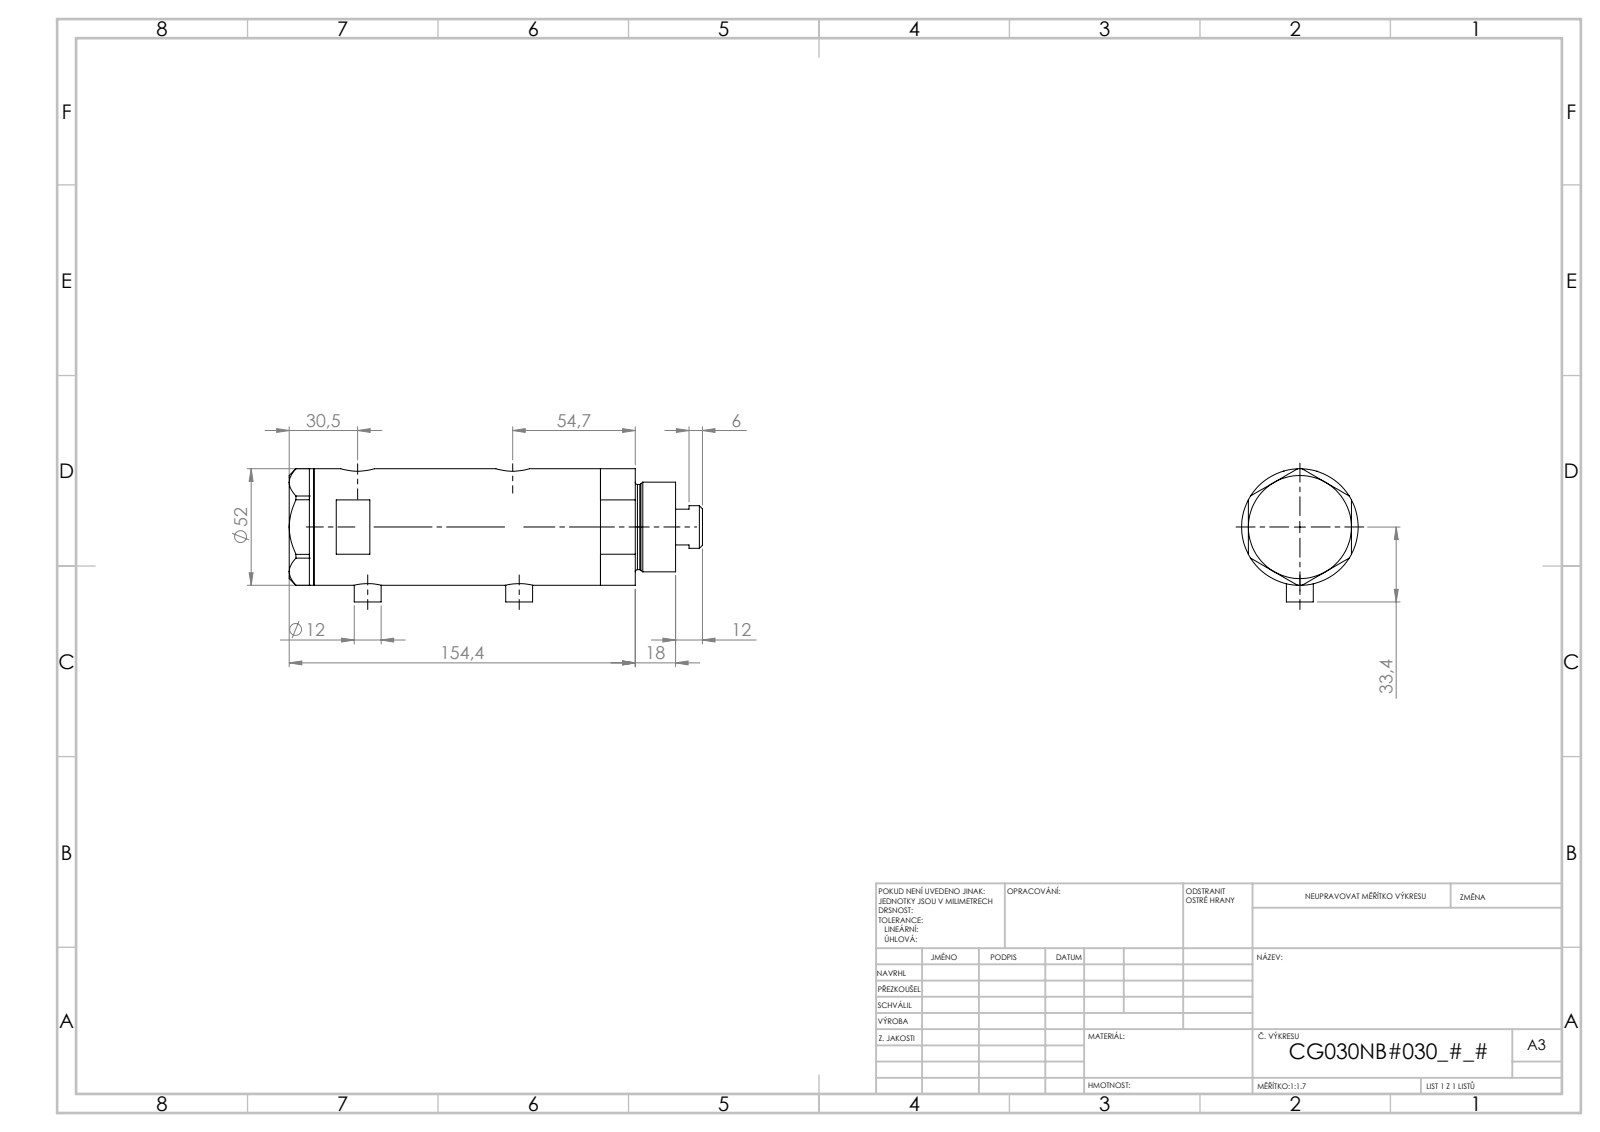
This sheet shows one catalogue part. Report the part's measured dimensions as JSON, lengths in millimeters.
{"part_name": "V270CG_BACK; V270CG_MIDDLE; V270CG_FRONT; V270CG_VC", "step_written_by": "SolidWorks 2019 (CONFIG_CONTROL_DESIGN)", "units": "millimeters", "bodies": {"solids": 4, "faces": 134, "planar": 65, "cylindrical": 49, "other": 20}, "overall_size": [184.4, 59.4, 52], "volume_mm3": 334920, "surface_area_mm2": 77135, "round_holes": [[9.73, 2], [12.5, 2], [15, 2], [6.5, 1], [20, 1], [21.5, 1], [30, 1], [33, 1], [44, 1]], "round_bosses_or_shafts": [[12, 2], [52, 1], [40, 1], [38, 1], [19, 1]], "face_to_face_distances": [91.5, 23.8, 67.7, 11, 34.8, 102.5, 46, 138.9, 127.9, 104.1], "hole_center_spacings": [2.9, 4.5, 64.7, 67.6, 69.2, 72.1]}
